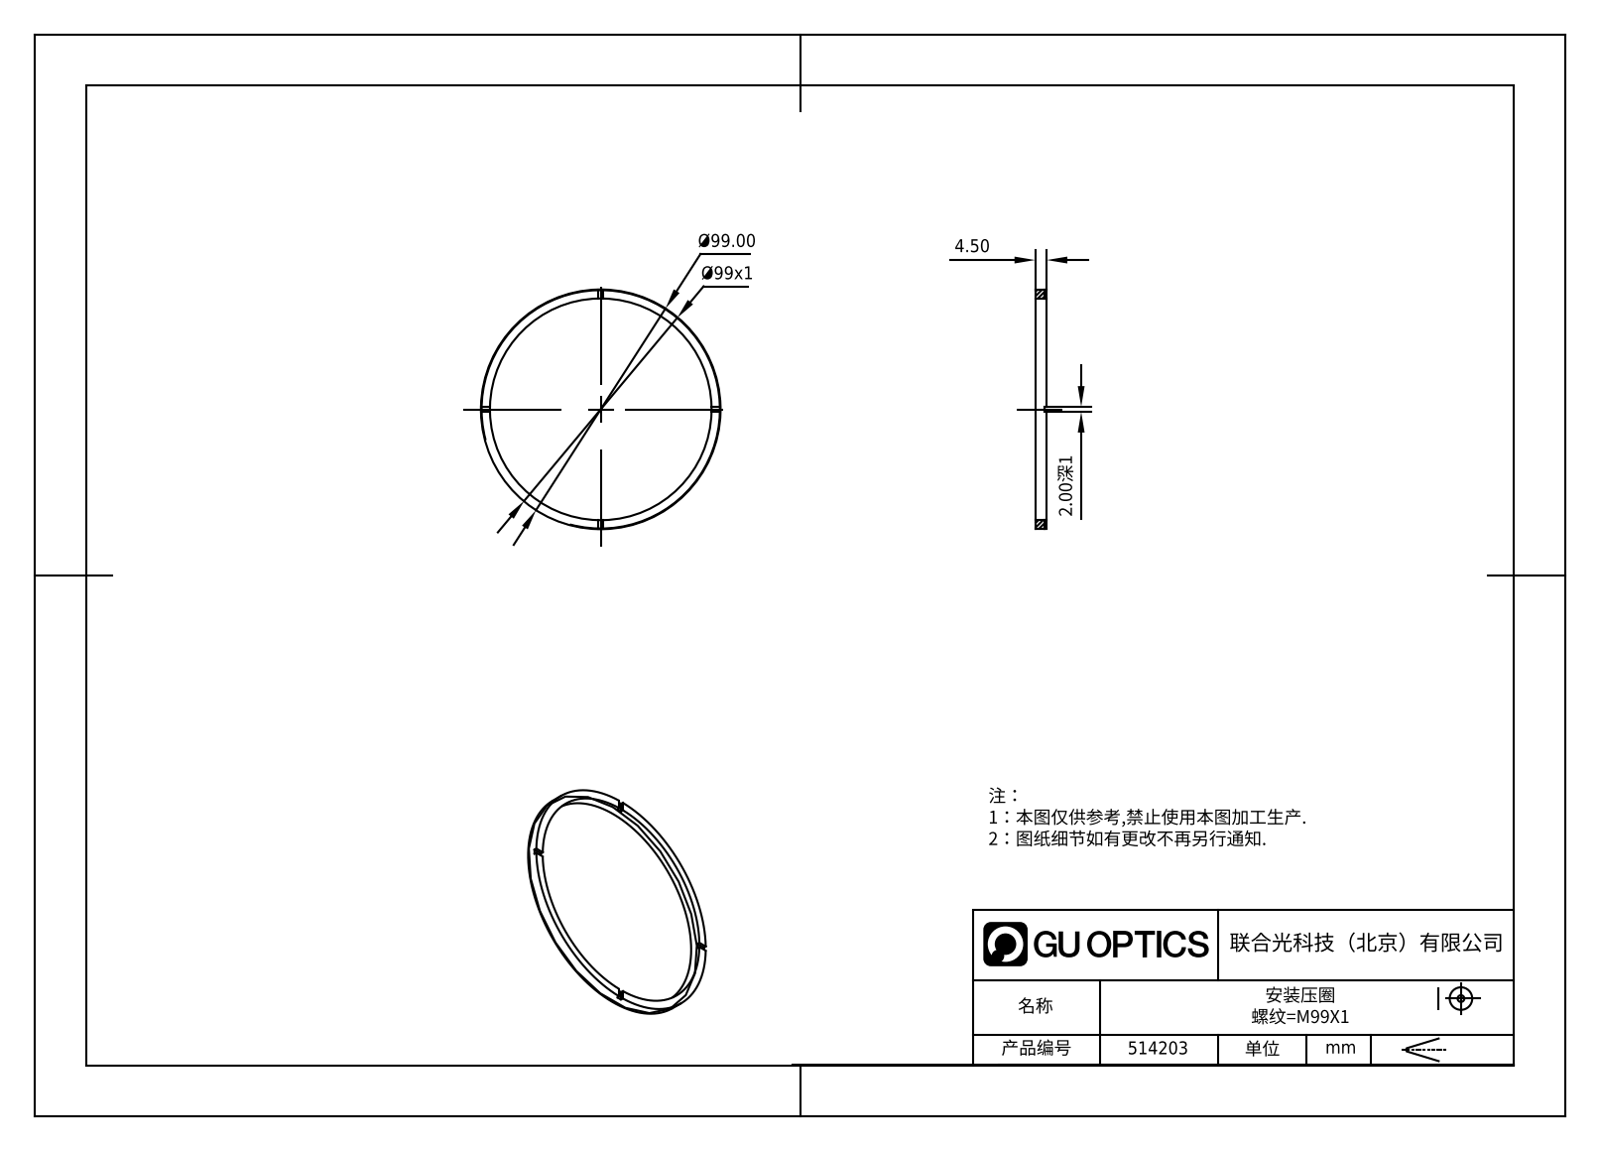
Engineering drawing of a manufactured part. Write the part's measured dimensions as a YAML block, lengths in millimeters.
part_name: "514203"
step_written_by: "SolidWorks 2020 (CONFIG_CONTROL_DESIGN)"
units: millimeters
bodies: {solids: 1, faces: 21, planar: 17, cylindrical: 4, other: 0}
overall_size: [99, 99, 4.5]
volume: 4697
surface_area: 4812
round_holes:
  - {diameter: 92, count: 1}
round_bosses_or_shafts:
  - {diameter: 99, count: 1}
face_to_face_distances: [4.5, 3.5, 1, 2]
